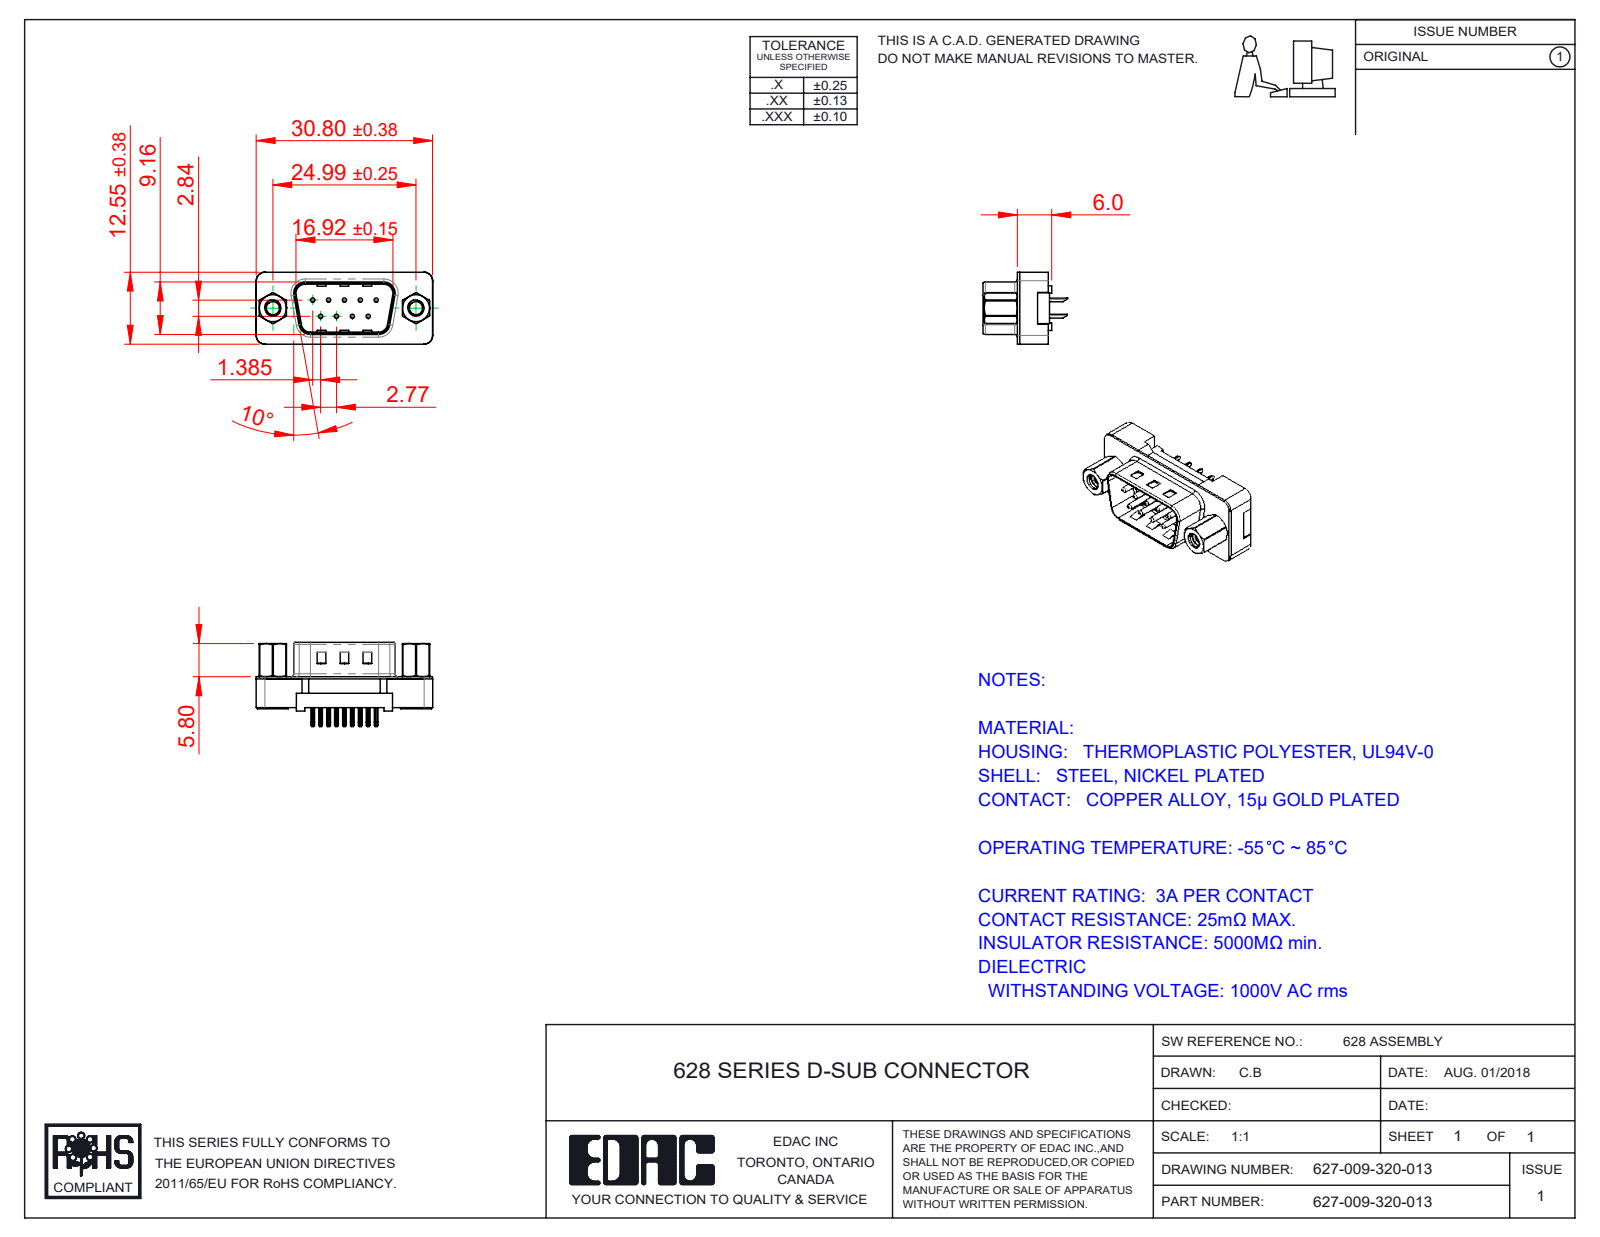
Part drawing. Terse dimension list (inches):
name: 627 Plastic Body Housing_09 Contacts; 627 PB 4-40 Threaded Rivet; 627 PB Contact Row 2_20; 627 4-40 Hex Standoff (+3 more)
written by: SolidWorks 2020 (CONFIG_CONTROL_DESIGN)
unit: in
bodies: 15 solids, 909 faces (503 planar, 312 cylindrical, 94 other)
size: 1.213 × 0.579 × 0.494
volume: 0.113 in³; area: 5.954 in²
holes: 9× ⌀0.014, 9× ⌀0.033, 2× ⌀0.089, 2× ⌀0.09, 2× ⌀0.157, 2× ⌀0.189, 2× ⌀0.197
bosses: 9× ⌀0.03, 2× ⌀0.193, 2× ⌀0.11
rounds: 18× R0.01, 9× R0.005, 8× R0.02, 7× R0.059, 4× R0.035, 4× R0.063, 4× R0.079, 2× R0.016
face distances: 0.016, 0.098, 0.213, 0.197, 0.114, 0.345, 0.083, 0.256, 0.027, 0.334
hole spacings: 0.124, 0.109, 0.198, 0.218, 0.295, 0.198, 0.279, 0.327
